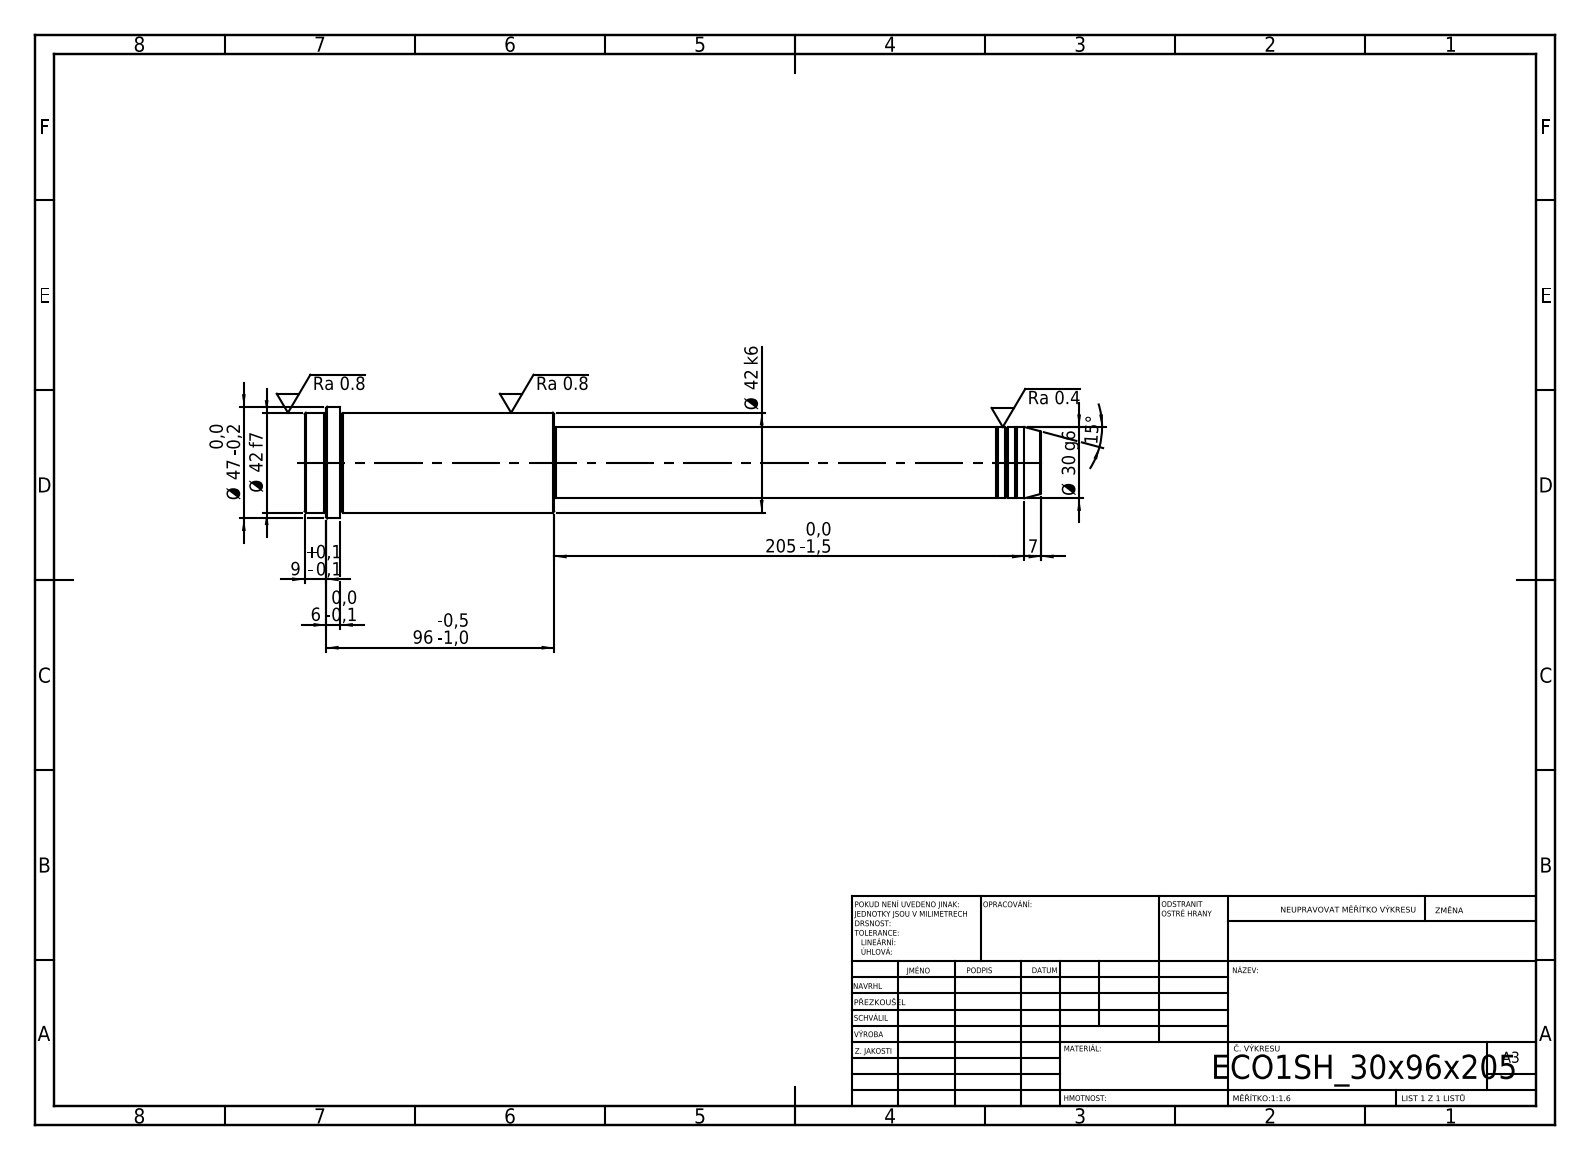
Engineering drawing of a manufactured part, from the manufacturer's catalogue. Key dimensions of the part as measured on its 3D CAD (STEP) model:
STEP written by: SolidWorks 2019 (CONFIG_CONTROL_DESIGN)
Units: millimetres
Bodies: 1 solid, 52 faces (6 planar, 16 cylindrical, 30 other)
Overall size (bounding box): 310 × 47 × 47
Volume: 291 570 mm³ · Surface area: 36 809 mm²
Round bosses / shafts (diameter × count): ⌀47 ×1, ⌀42 ×1, ⌀30 ×1, ⌀29 ×1
Main face-to-face distances: 105, 205, 310, 295, 90, 15, 301, 96, 6, 9
